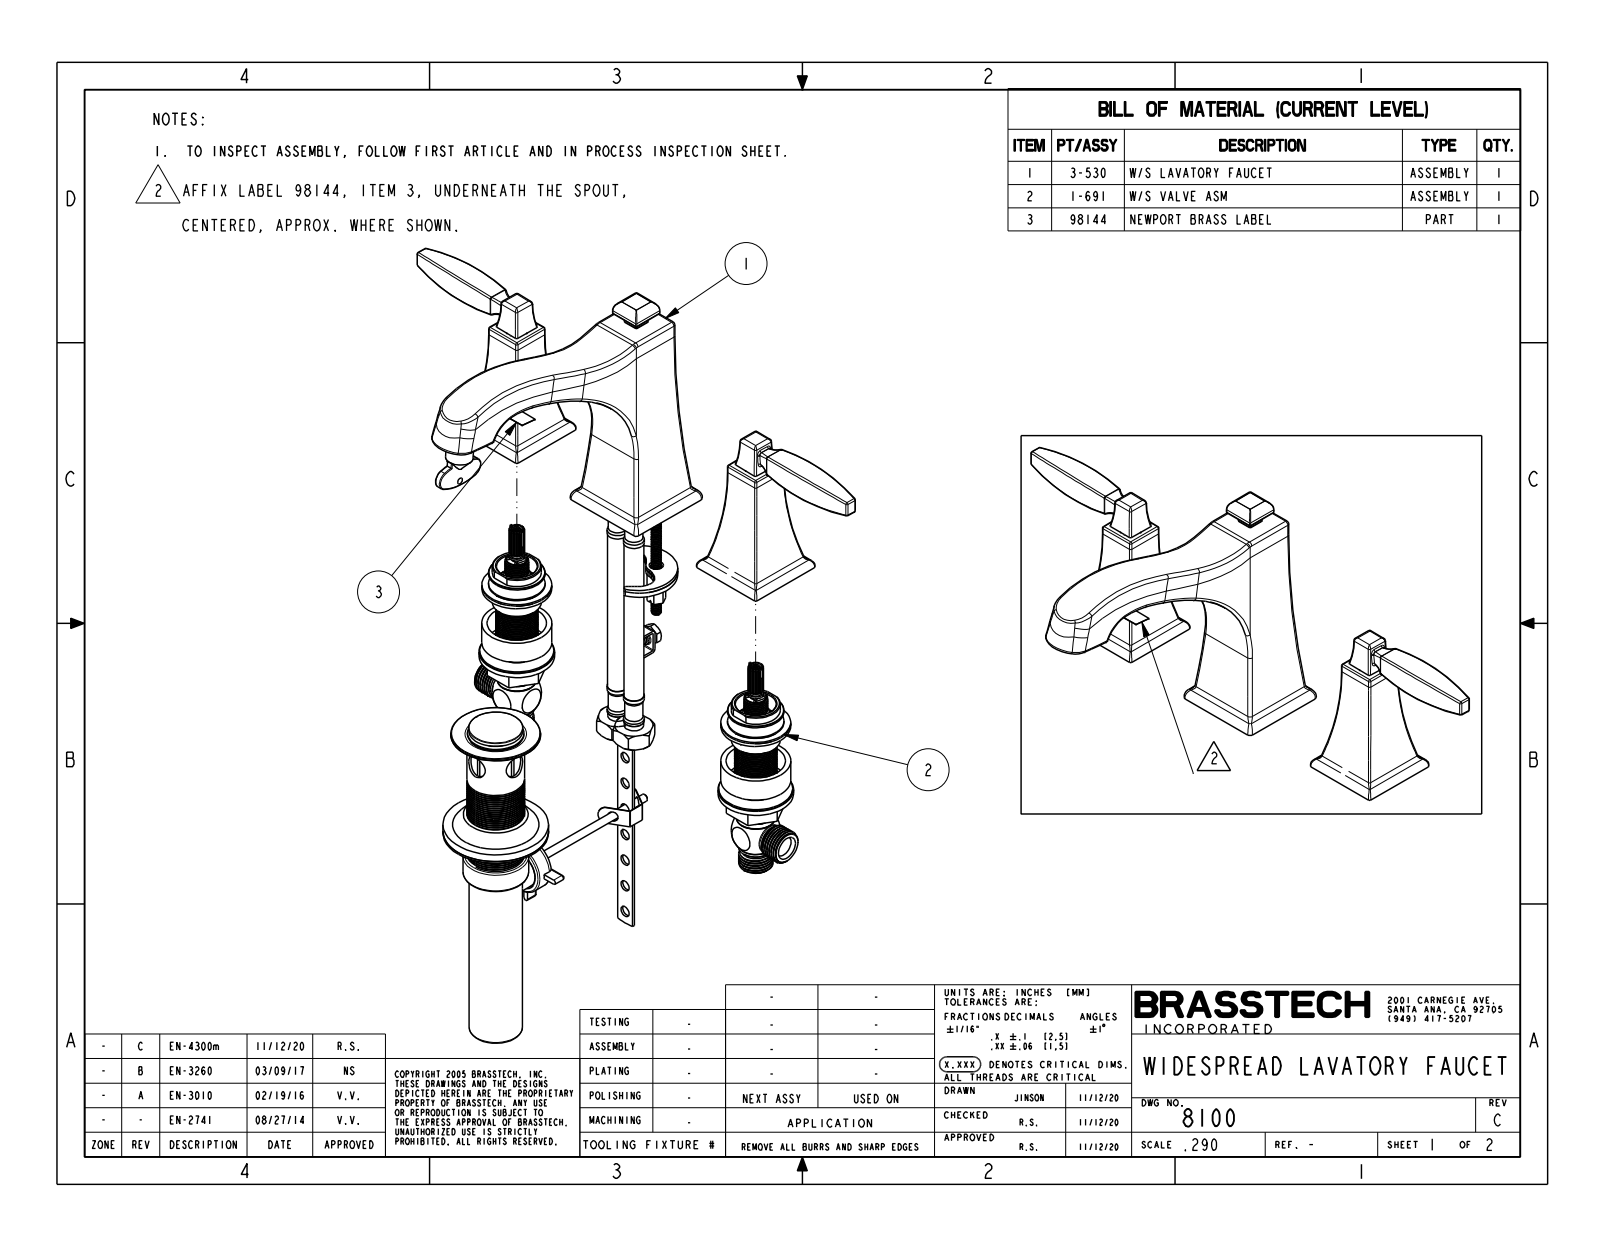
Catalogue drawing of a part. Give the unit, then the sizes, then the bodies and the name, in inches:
Units: inches
Overall size (bounding box): 14.499 × 7.683 × 5.764
Round bosses / shafts (diameter × count): ⌀0.63 ×2
Partial cylindrical surfaces — rounded edges, fillets, slot ends (radius × count): R0.039 ×38, R0.02 ×16, R0.079 ×13, R0.157 ×10, R0.632 ×8, R2.953 ×8, R0.197 ×6, R9.229 ×6
Main face-to-face distances: 5.118, 5.114, 2.964, 2.96, 2.154, 0.965, 1.339, 2.983, 2.98, 0.02
Volume: 31.58 in³ · Surface area: 119.5 in²
Bodies: 3 solids, 389 faces (40 planar, 142 cylindrical, 207 other)
Part name (STEP PRODUCT): 8100
STEP written by: CREO PARAMETRIC BY PTC INC, 2018400 (CONFIG_CONTROL_DESIGN)
